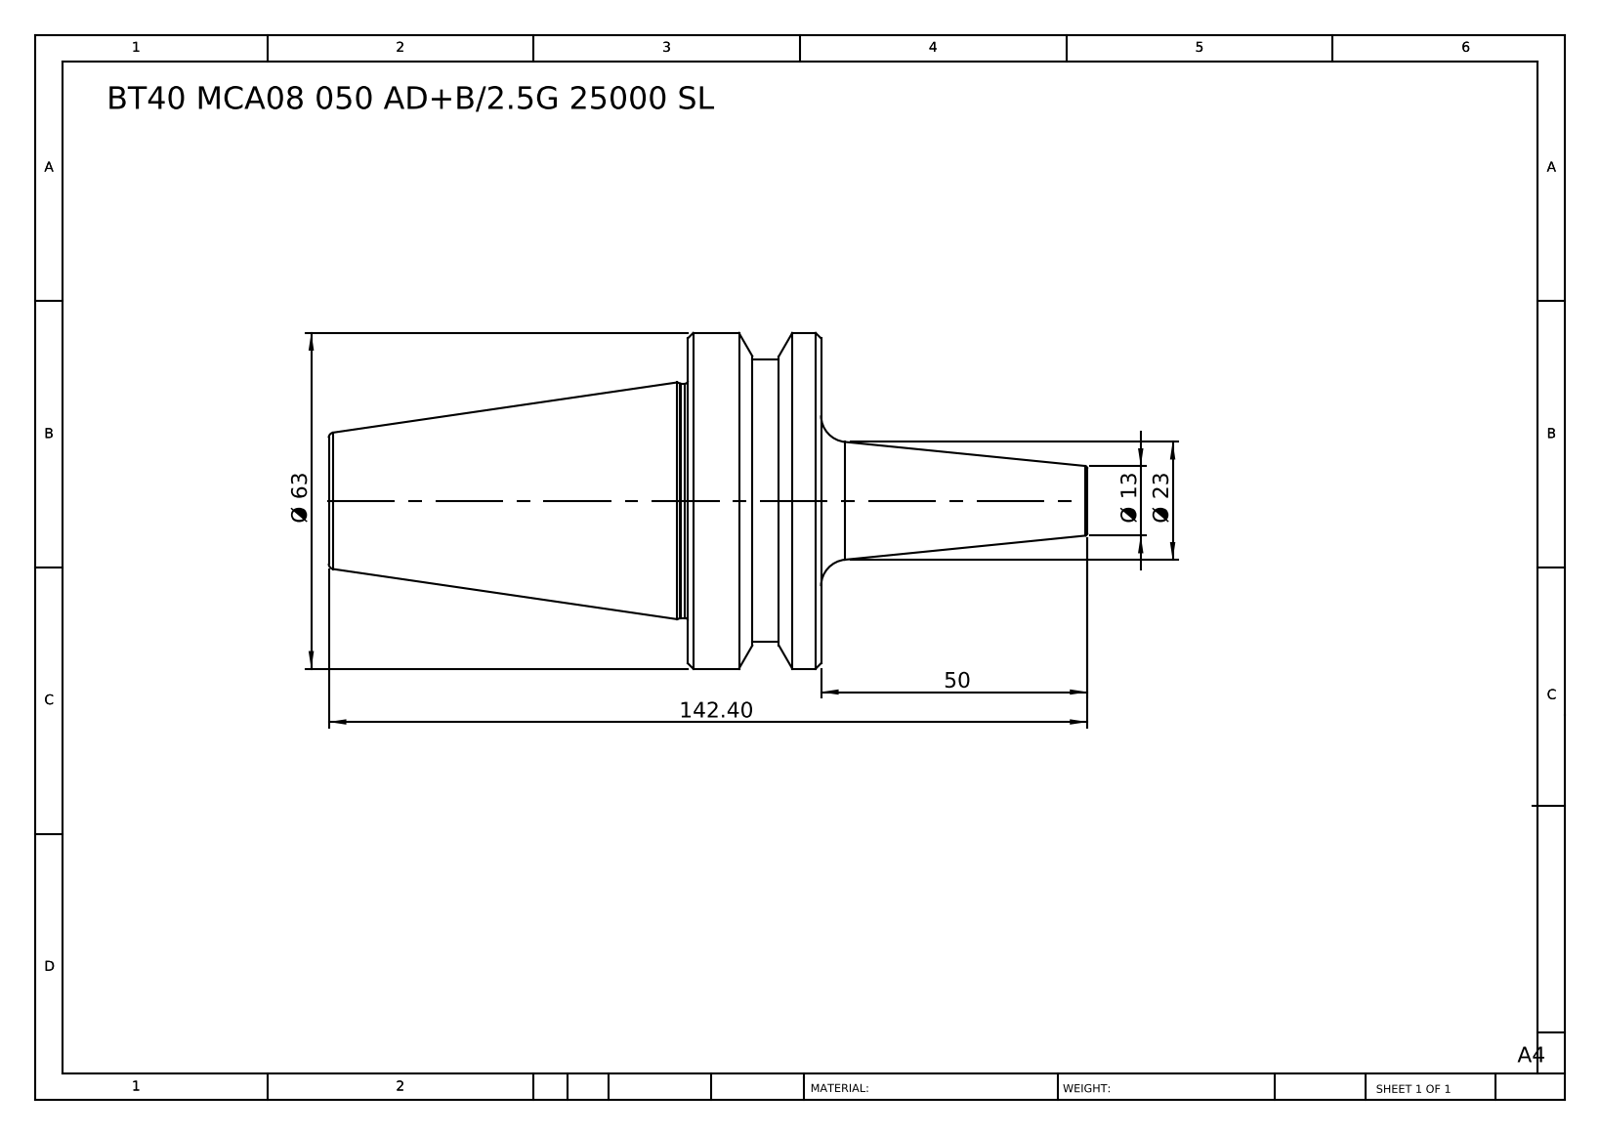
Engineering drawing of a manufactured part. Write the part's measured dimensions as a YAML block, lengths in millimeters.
part_name: "BT40 MCA08 050 AD+B-2.5G 25000 SL"
step_written_by: "SolidWorks 2014 (CONFIG_CONTROL_DESIGN)"
units: millimeters
bodies: {solids: 1, faces: 38, planar: 6, cylindrical: 8, other: 24}
overall_size: [142.4, 63, 63]
volume: 151726
surface_area: 20772
round_bosses_or_shafts:
  - {diameter: 63, count: 1}
  - {diameter: 53, count: 1}
  - {diameter: 44, count: 1}
face_to_face_distances: [25, 92.4, 67.4, 50, 75, 142.4, 62.9, 12.9, 12.1, 79.5]
